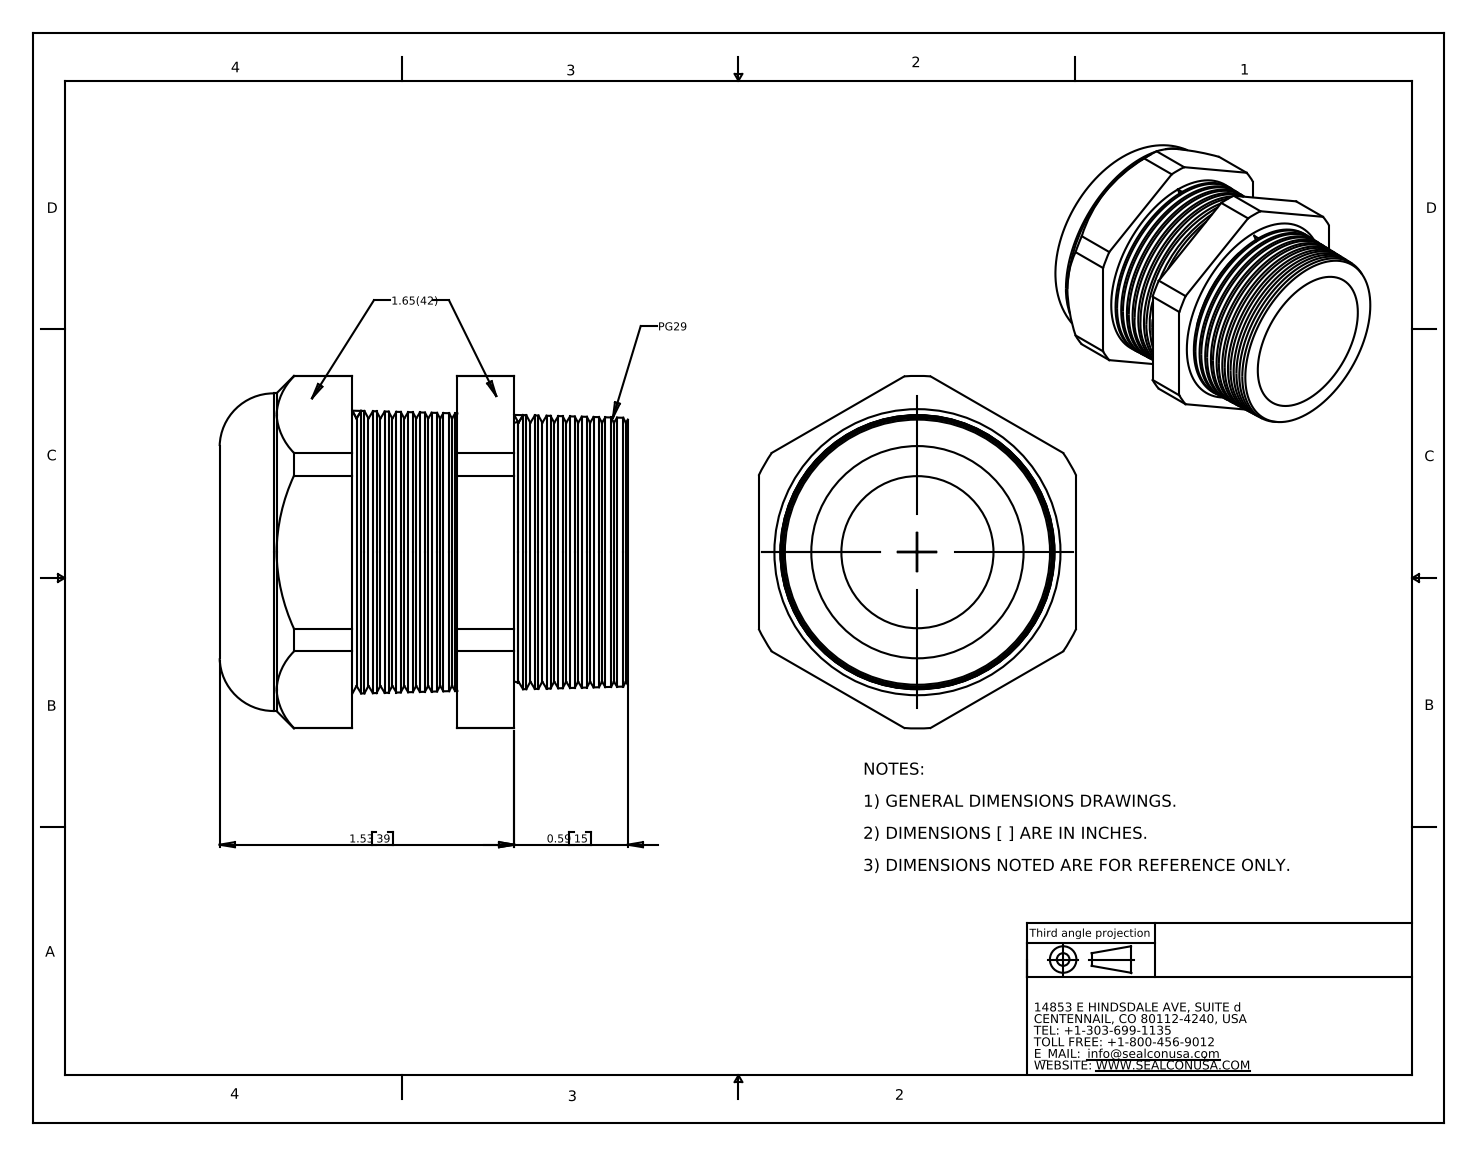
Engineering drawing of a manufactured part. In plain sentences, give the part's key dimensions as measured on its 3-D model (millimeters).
The part is named "CD29CR-BK". Its 3-D file was written by "SolidWorks 2007 (CONFIG_CONTROL_DESIGN)". It is 2 solids with 169 faces: 19 planar, 22 cylindrical and 128 other. Overall it measures 53.8 by 46.5 by 41.9 millimeters. Its volume is 41 900 cubic millimeters and its surface area 16 970 square millimeters. Round holes: 1 of diameter 20.1, 1 of diameter 28. Round bosses or shafts: 1 of diameter 41.9. Partial cylindrical surfaces (rounded edges, fillets, slot ends): 1 of radius 23.3. The main face-to-face distances are 41.9, 23.9, 10, 13.9, 31.4, 21.4, 7.5, 46.4, 36.3, 22.5.
